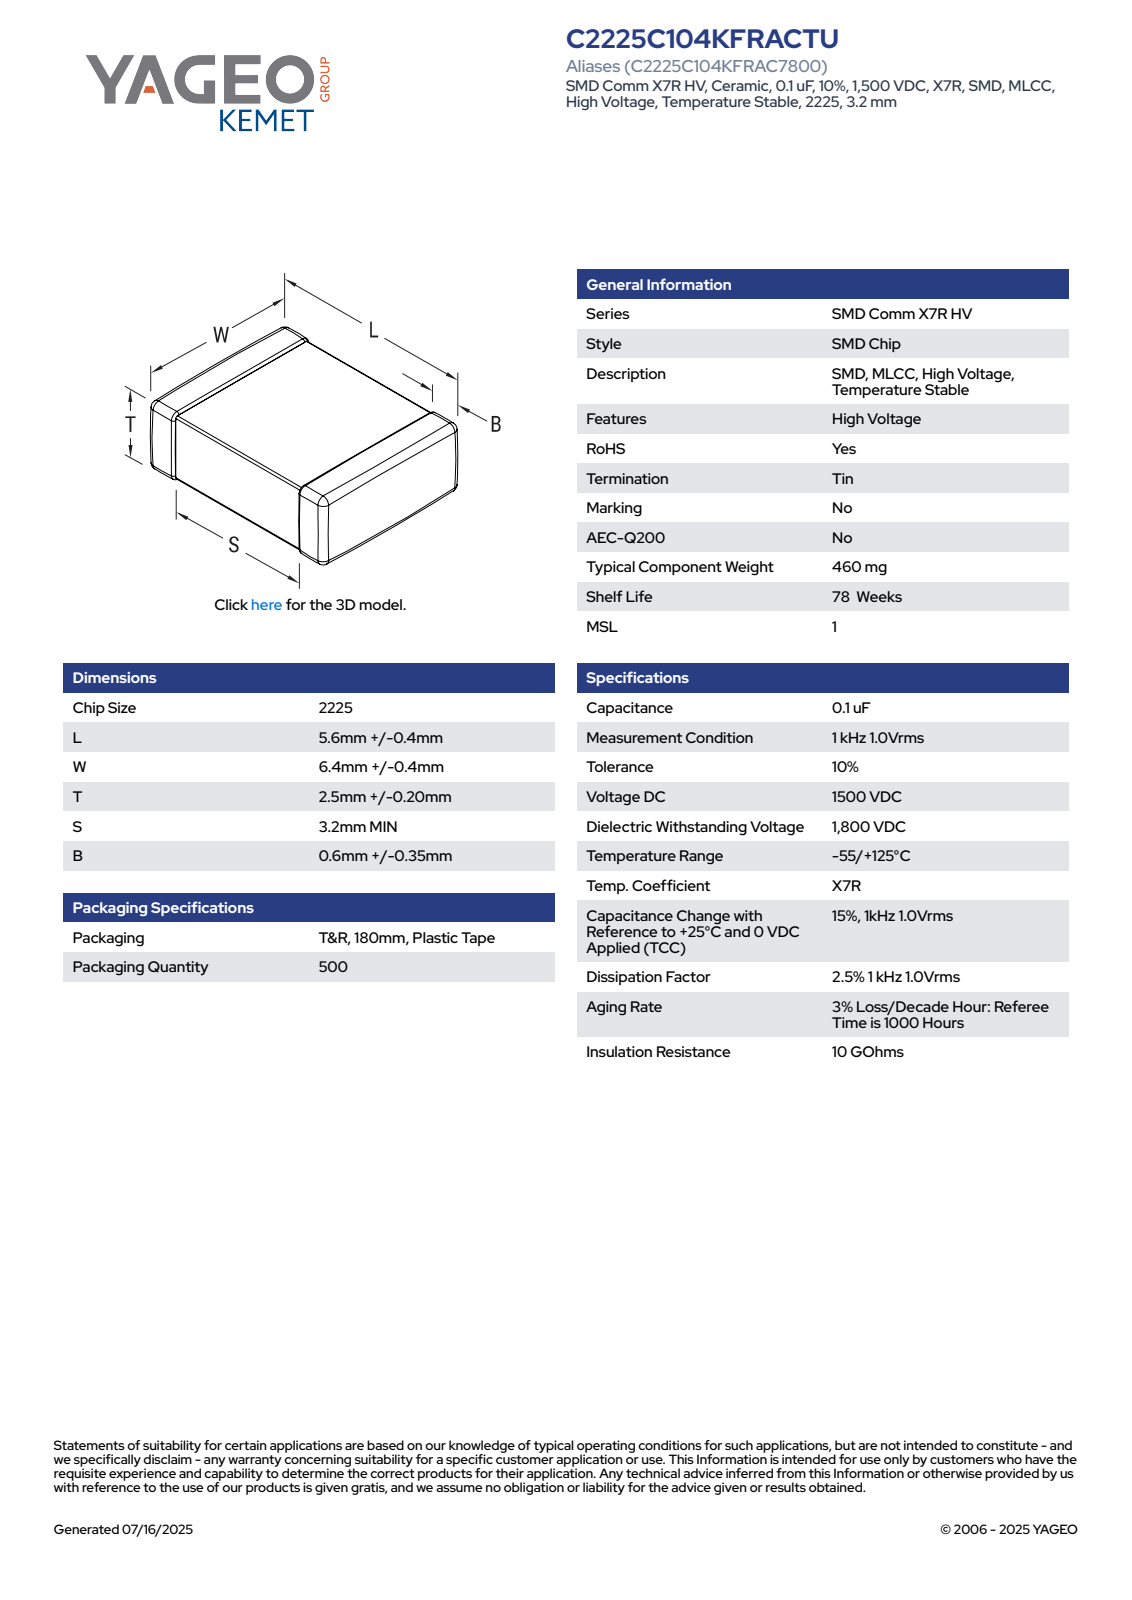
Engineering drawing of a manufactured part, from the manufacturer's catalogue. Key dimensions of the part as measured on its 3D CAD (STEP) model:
Part name (STEP PRODUCT): CCS_CCSTDNOS_2225_L6W6.8T2.7B0.95
STEP written by: SolidWorks 2014 (AUTOMOTIVE_DESIGN)
Units: millimetres
Bodies: 4 solids, 125 faces (71 planar, 38 cylindrical, 16 other)
Overall size (bounding box): 6.8 × 6 × 2.7
Volume: 99 mm³ · Surface area: 146 mm²
Partial cylindrical surfaces — rounded edges, fillets, slot ends (radius × count): R0.14 ×24
Main face-to-face distances: 2.42, 2.56, 6, 6.52, 2.7, 6.66, 6.8, 3.33, 0.43, 3.47
